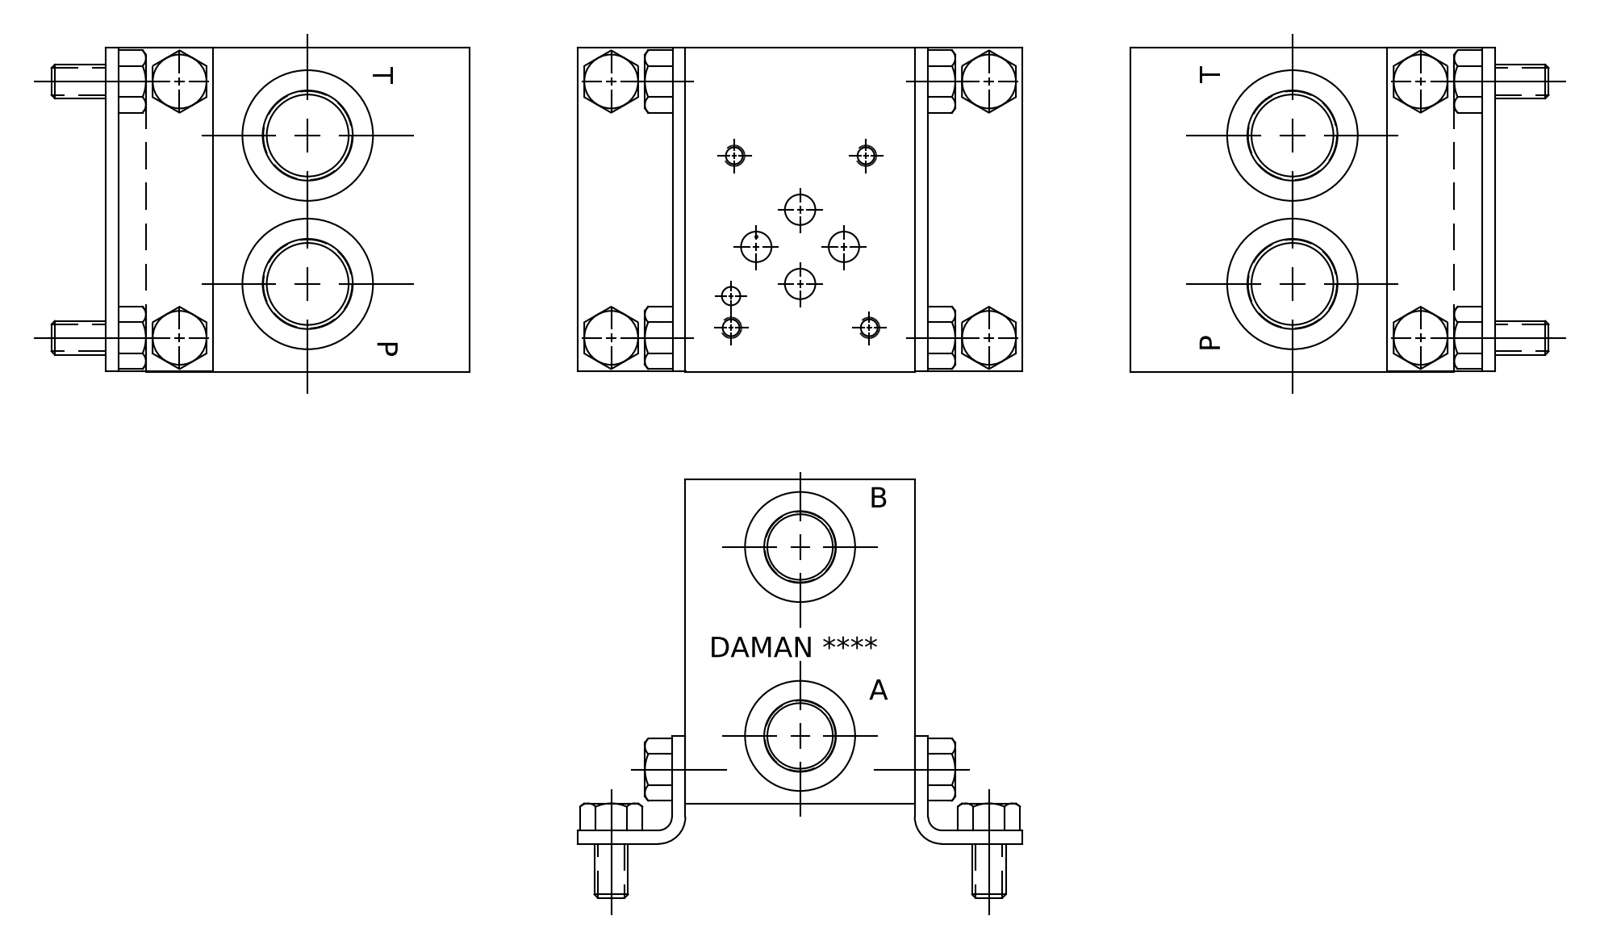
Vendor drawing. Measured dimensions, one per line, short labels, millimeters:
name: Part_AD03P012B_3D
written by: Autodesk Inventor 2020 (CONFIG_CONTROL_DESIGN)
unit: mm
bodies: 1 solid, 499 faces (306 planar, 45 cylindrical, 148 other)
size: 76.2 × 76.2 × 53.98
volume: 264 822 mm³; area: 39 212 mm²
holes: 4× ⌀4.22, 4× ⌀5, 3× ⌀7.14, 2× ⌀6.76, 2× ⌀8, 2× ⌀12.7, 2× ⌀15.06, 2× ⌀16.76, 2× ⌀17.48, 2× ⌀18.92, 2× ⌀21.06, 2× ⌀25.93
face distances: 76.2, 53.98, 0.79, 53.19, 52.4, 75.41, 0.75, 76.16, 17.37, 36.6
hole spacings: 19.95, 22.05, 33.55, 40.49, 51.45, 7.49, 12.99, 13.51
